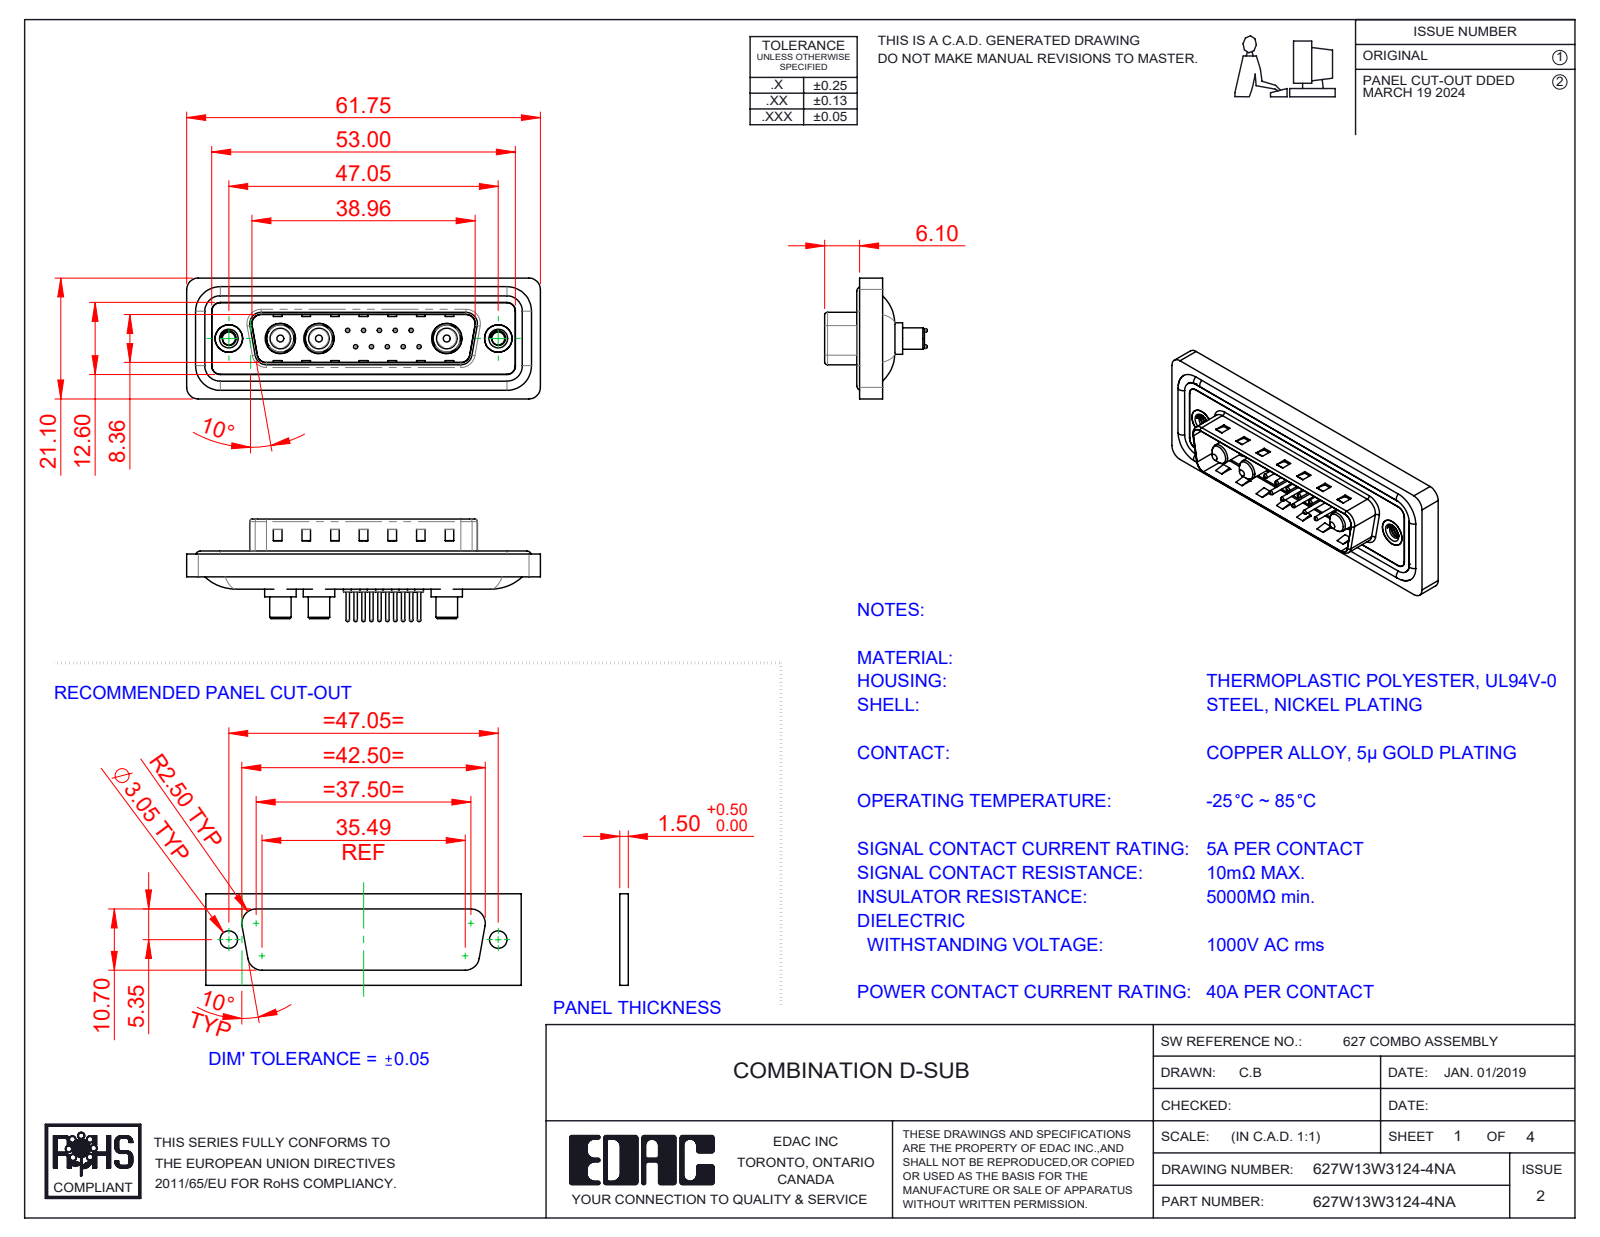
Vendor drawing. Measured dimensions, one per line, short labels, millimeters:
name: 627Combo Contact Row 2_24; 627W13W3124-4NA; 627Combo Threaded Rivet_A; 627Combo Housing_13W3 (+5 more)
written by: SolidWorks 2023 (CONFIG_CONTROL_DESIGN)
unit: mm
bodies: 23 solids, 968 faces (309 planar, 387 cylindrical, 272 other)
size: 61.75 × 21.1 × 17.9
volume: 7 392 mm³; area: 11 905 mm²
holes: 10× ⌀0.75, 10× ⌀1.6, 10× ⌀2, 3× ⌀4.85, 3× ⌀5.3, 2× ⌀2.26, 2× ⌀4, 2× ⌀4.8, 2× ⌀5
bosses: 10× ⌀1.5, 10× ⌀0.6, 4× ⌀1.6, 3× ⌀5.5, 3× ⌀5.2, 3× ⌀4.75, 3× ⌀3.75, 3× ⌀3.6
rounds: 22× R1.5, 18× R2, 8× R0.5, 8× R1.6, 4× R0.25, 4× R0.6, 4× R0.65, 4× R0.9
face distances: 0.4, 1.5, 1.1, 1.6, 0.5, 3.1, 2.9, 0.82, 9.58, 4.1
hole spacings: 3.16, 2.77, 5.04, 5.54, 7.49, 5.03, 8.31, 10.11
